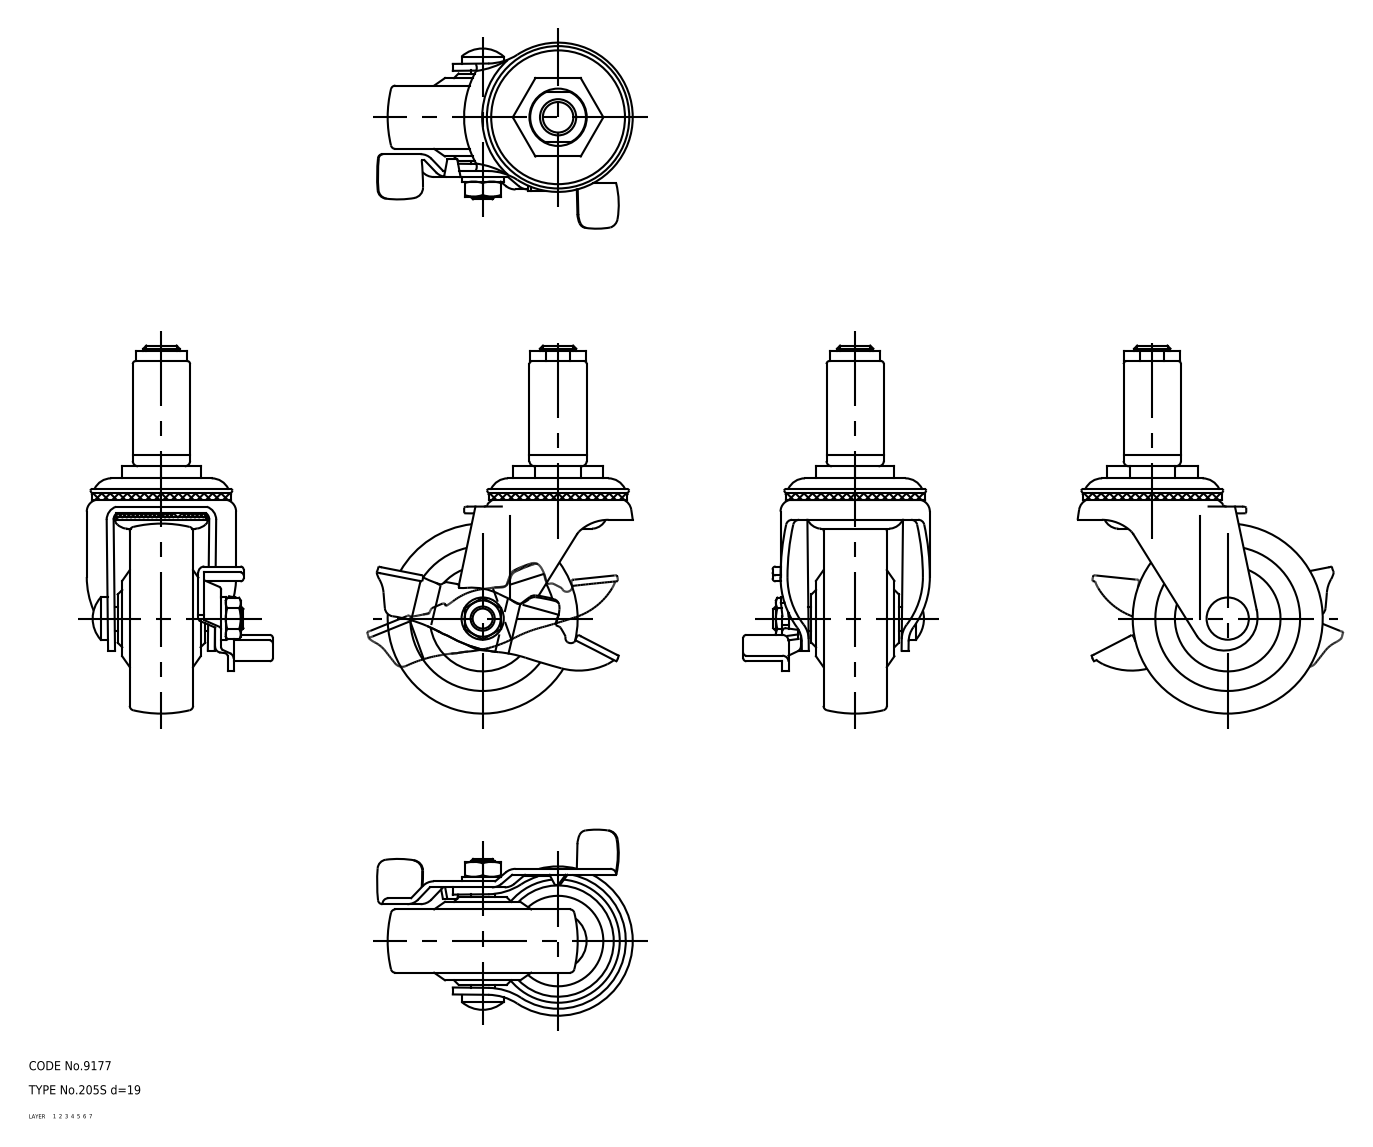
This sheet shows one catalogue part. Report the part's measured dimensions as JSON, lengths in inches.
{"part_name": "wheel; main shaft; lever; axle (+1 more)", "step_written_by": "CADfix (AUTOMOTIVE_DESIGN)", "units": "inches", "bodies": {"solids": 5, "faces": 332, "planar": 0, "cylindrical": 0, "other": 332}, "overall_size": [4.803, 3.342, 2.446], "volume_in3": 6.601, "surface_area_in2": 54.28}
